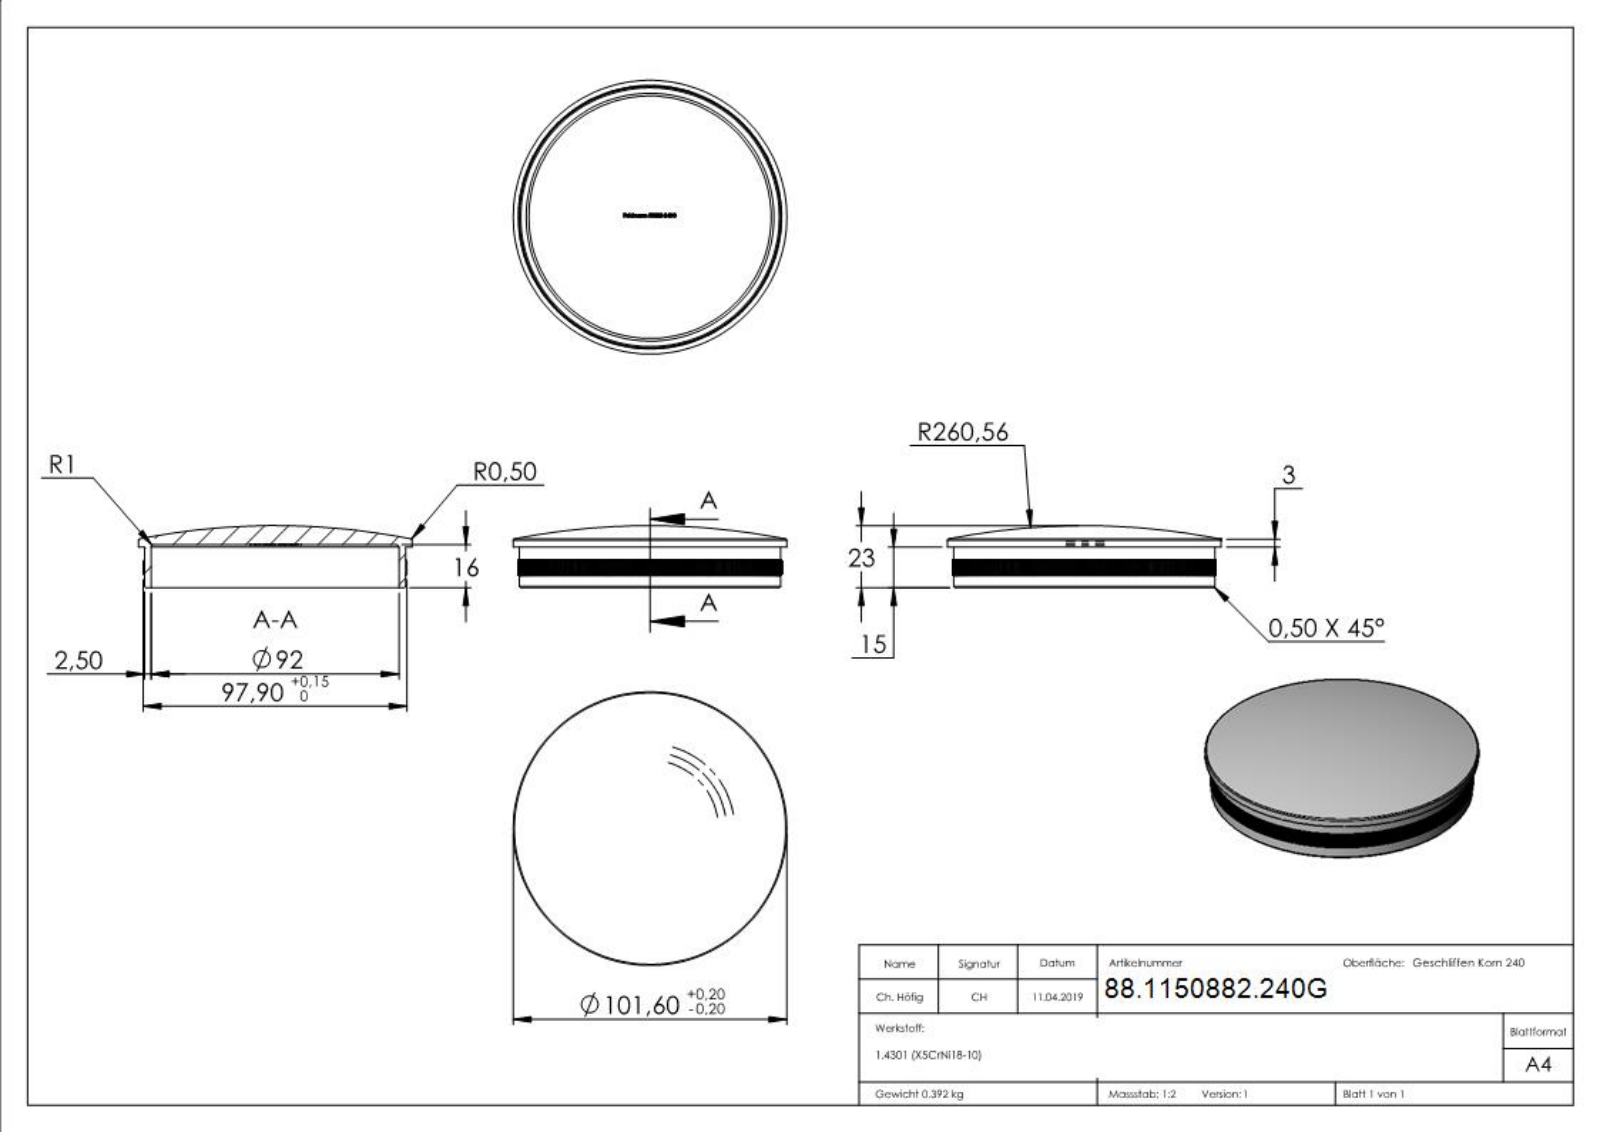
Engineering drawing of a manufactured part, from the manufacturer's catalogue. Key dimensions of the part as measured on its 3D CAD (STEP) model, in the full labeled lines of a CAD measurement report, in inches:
Part name (STEP PRODUCT): 50882-240G
STEP written by: SolidWorks 2015 (CONFIG_CONTROL_DESIGN)
Units: inches
Bodies: 1 solid, 3069 faces (1244 planar, 568 cylindrical, 1257 other)
Overall size (bounding box): 4 × 4 × 0.906
Volume: 3.024 in³ · Surface area: 43.18 in²
Round holes (diameter × count): ⌀3.622 ×1
Round bosses / shafts (diameter × count): ⌀4 ×1, ⌀3.819 ×1
Partial cylindrical surfaces — rounded edges, fillets, slot ends (radius × count): R1.927 ×1
Main face-to-face distances: 0.039, 0.591, 0.63, 1.909, 1.91, 1.909, 1.911, 1.908, 1.907, 1.912
